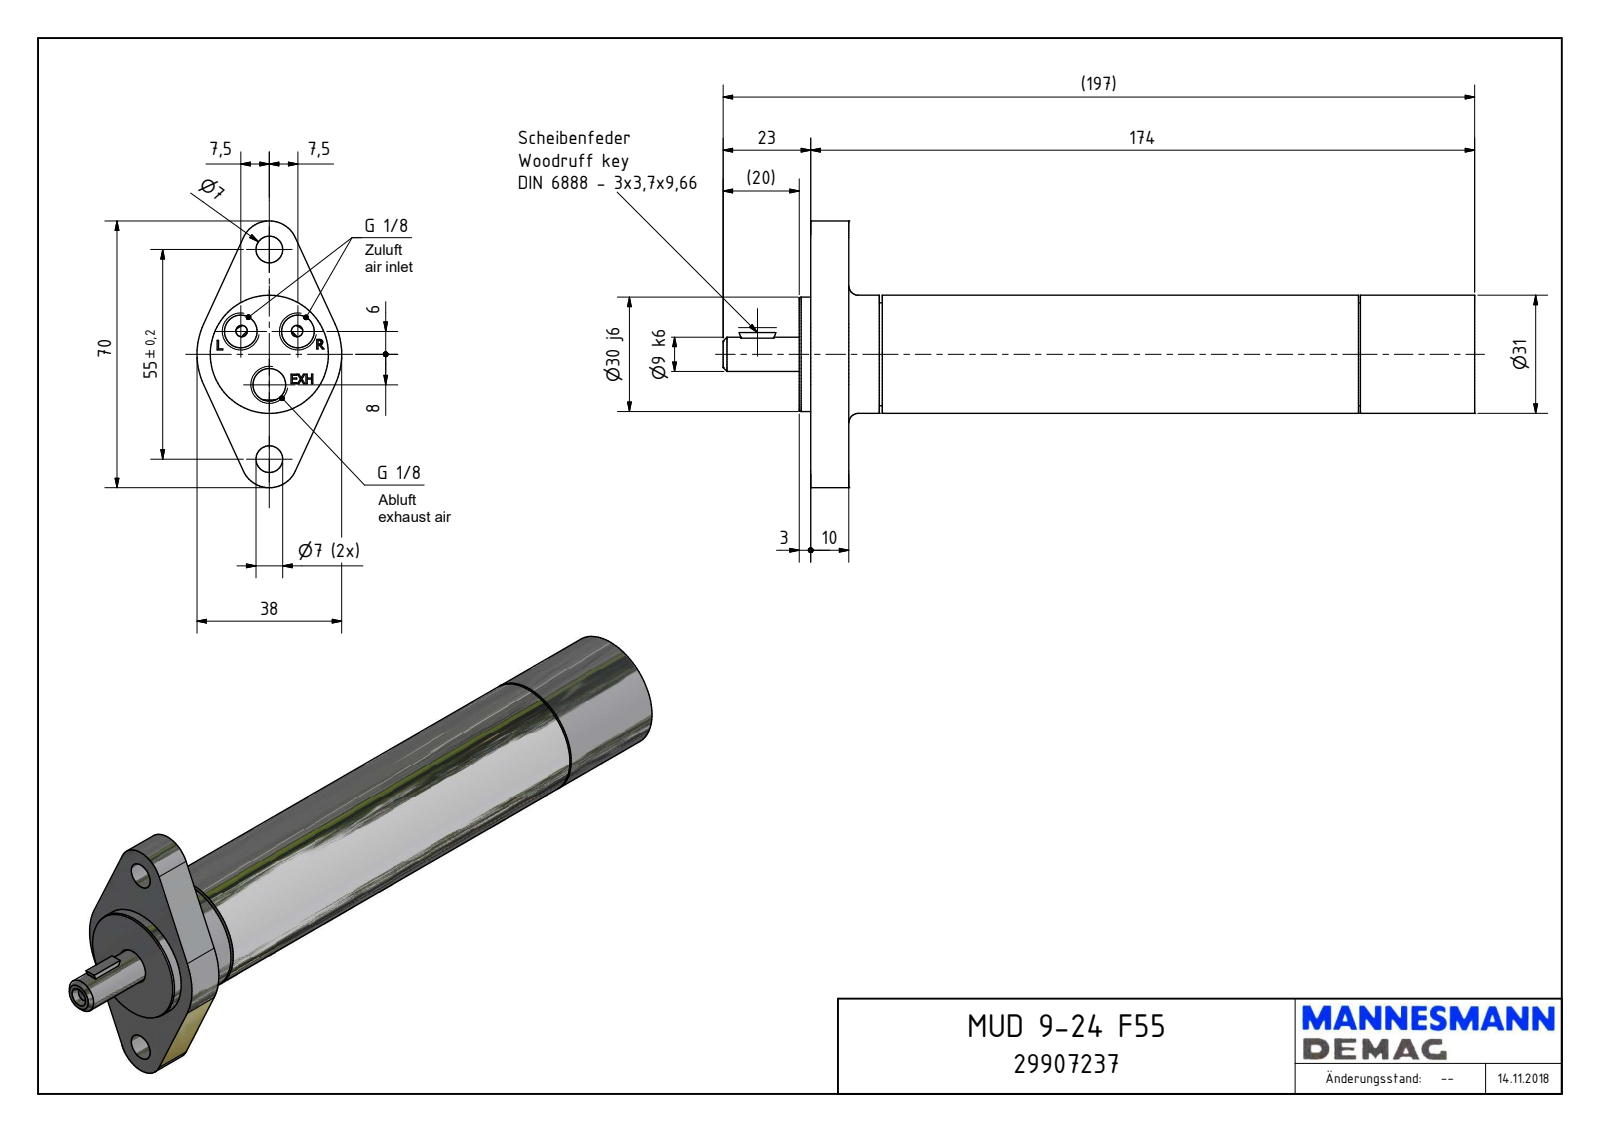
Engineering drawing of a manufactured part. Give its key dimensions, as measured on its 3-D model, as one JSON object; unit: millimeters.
{"part_name": "MUD 9-24 F55_29907237", "step_written_by": "Autodesk Inventor 2018 (AUTOMOTIVE_DESIGN)", "units": "millimeters", "bodies": {"solids": 1, "faces": 155, "planar": 91, "cylindrical": 28, "other": 36}, "overall_size": [197.3, 70, 38], "volume_mm3": 142242, "surface_area_mm2": 24731, "round_holes": [[8.57, 3], [7, 2], [1, 1], [9.5, 1], [10.36, 1], [13.36, 1], [16, 1]], "round_bosses_or_shafts": [[31, 1], [30, 1], [27, 1], [9, 1]], "partial_cylinders_radius": [[7.5, 2], [5, 1], [5.25, 1], [19, 1]], "face_to_face_distances": [10, 3, 13, 174.3, 177.3, 164.3, 37.98, 8, 0.5, 144.3], "hole_center_spacings": [9.6, 15.88, 22.77, 27.5, 34.33, 8, 15, 19.5]}
